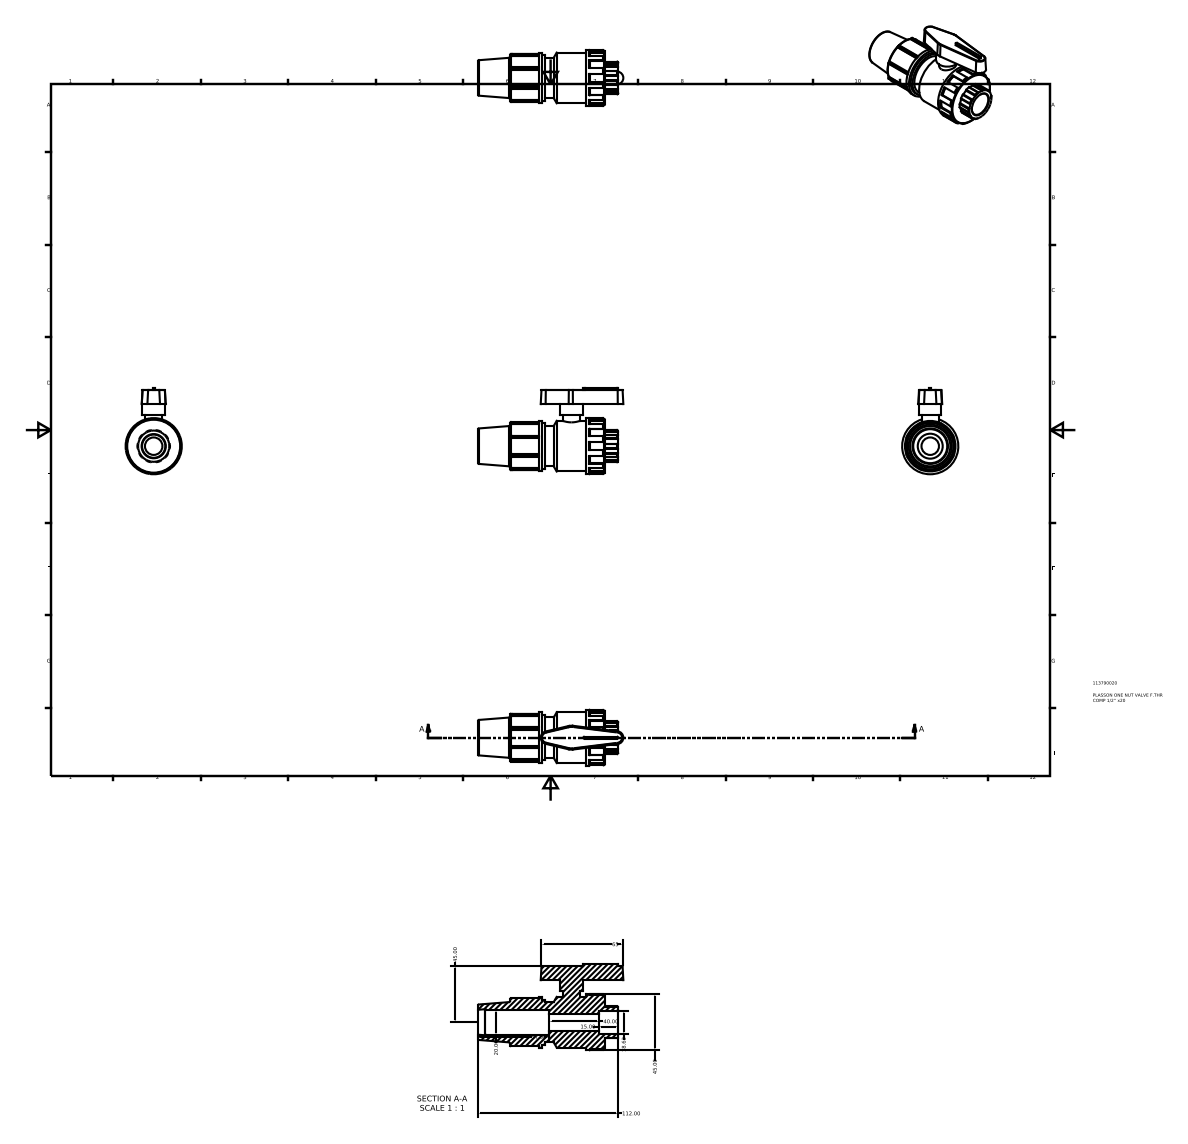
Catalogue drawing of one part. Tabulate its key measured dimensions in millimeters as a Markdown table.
| quantity | value |
| --- | --- |
| part name | 113790020 |
| STEP written by | Autodesk Inventor 2015 (AUTOMOTIVE_DESIGN) |
| units | millimeters |
| bodies | 1 solid, 248 faces (99 planar, 74 cylindrical, 75 other) |
| overall size | 116.26 × 68.85 × 45 |
| volume | 102 984 mm³ |
| surface area | 26 750 mm² |
| round holes (diameter × count) | 14 × 1, 18.63 × 1, 20 × 1 |
| round bosses / shafts (diameter × count) | 45 × 1, 43.2 × 1, 40.5 × 1, 38.48 × 1, 36.45 × 1, 32.4 × 1, 18 × 1, 13.5 × 1 |
| partial cylindrical surfaces (radius × count) | 0.56 × 20, 0.6 × 16, 0.37 × 4, 0.9 × 2, 12.48 × 1, 13.04 × 1 |
| main face-to-face distances | 11.25, 15, 10.5, 25.65, 86.5, 101.5, 51.3, 35.2, 50.2, 53.33 |
